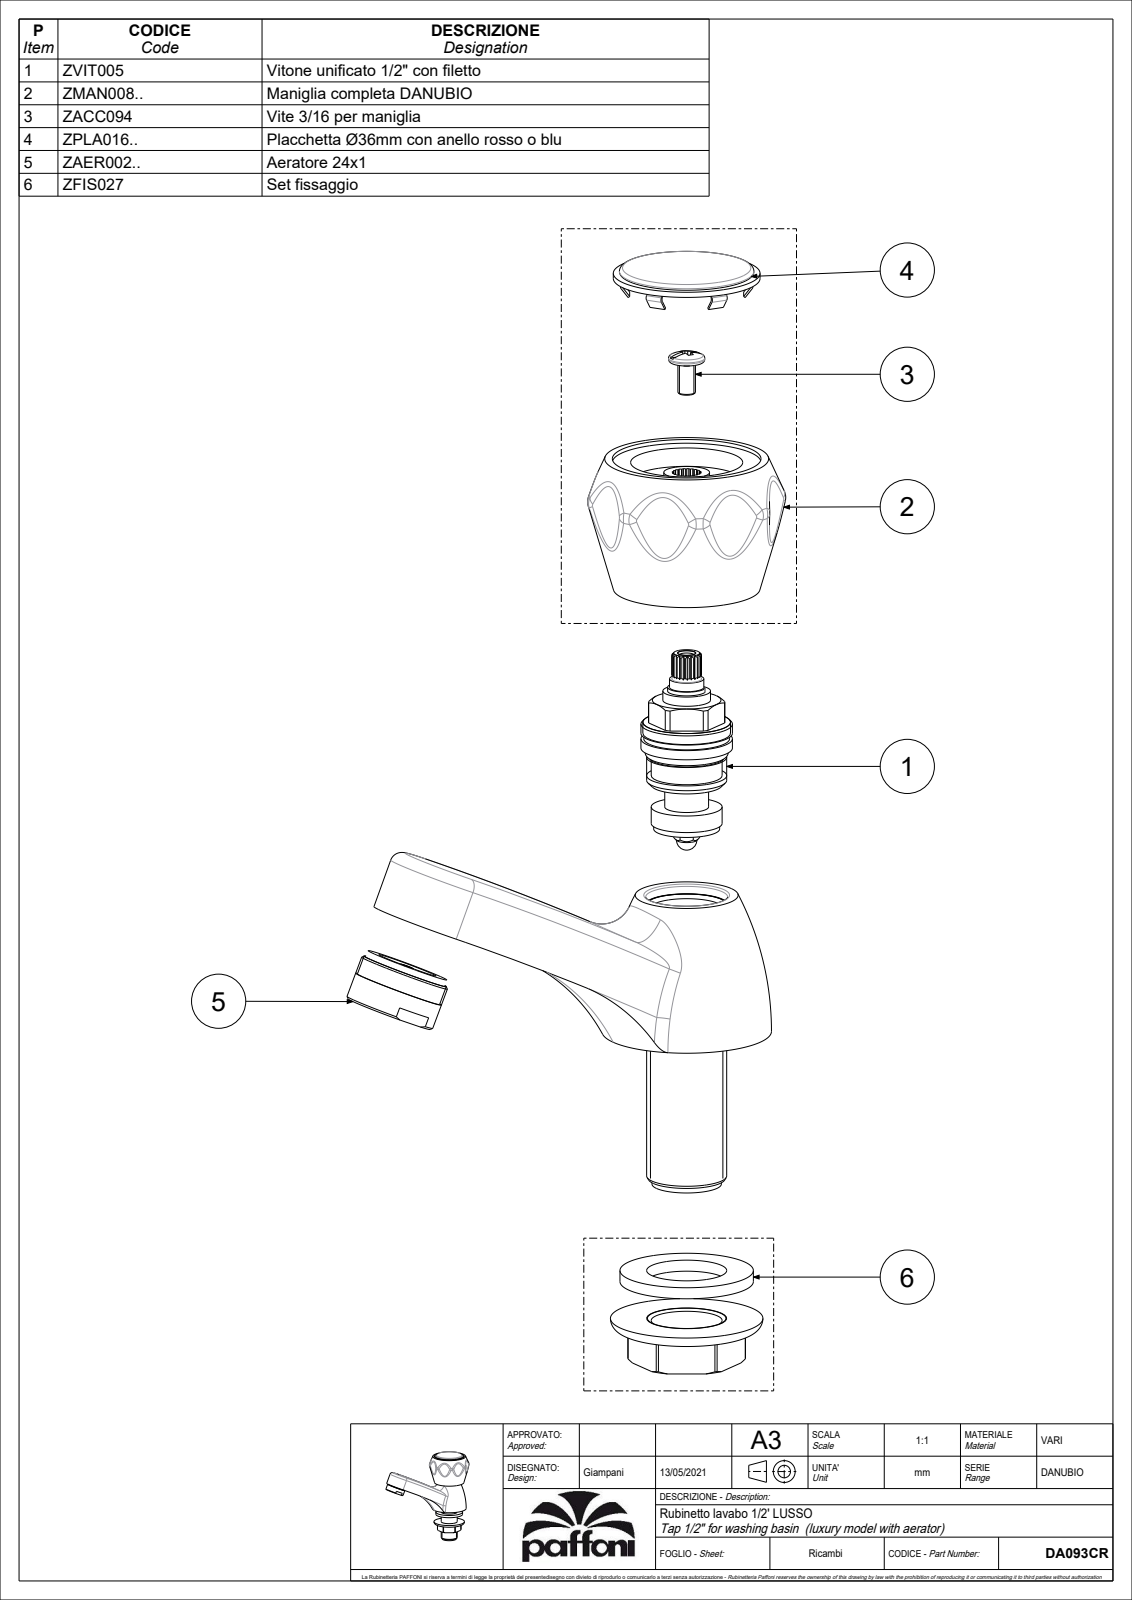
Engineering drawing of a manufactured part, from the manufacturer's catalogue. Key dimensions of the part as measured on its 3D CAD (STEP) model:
Part name (STEP PRODUCT): DA093CR
STEP written by: CREO PARAMETRIC BY PTC INC, 2020044 (CONFIG_CONTROL_DESIGN)
Units: millimetres
Bodies: 1 solid, 99 faces (11 planar, 15 cylindrical, 73 other)
Overall size (bounding box): 118.52 × 74 × 49.27
Volume: 146 128 mm³ · Surface area: 20 749 mm²
Round bosses / shafts (diameter × count): ⌀38.5 ×1, ⌀24 ×1
Partial cylindrical surfaces — rounded edges, fillets, slot ends (radius × count): R21.31 ×8, R15 ×1, R979.65 ×1, R995.65 ×1
Main face-to-face distances: 30, 35.3, 70.6, 71, 35.7, 0.4, 4, 26, 22, 3
